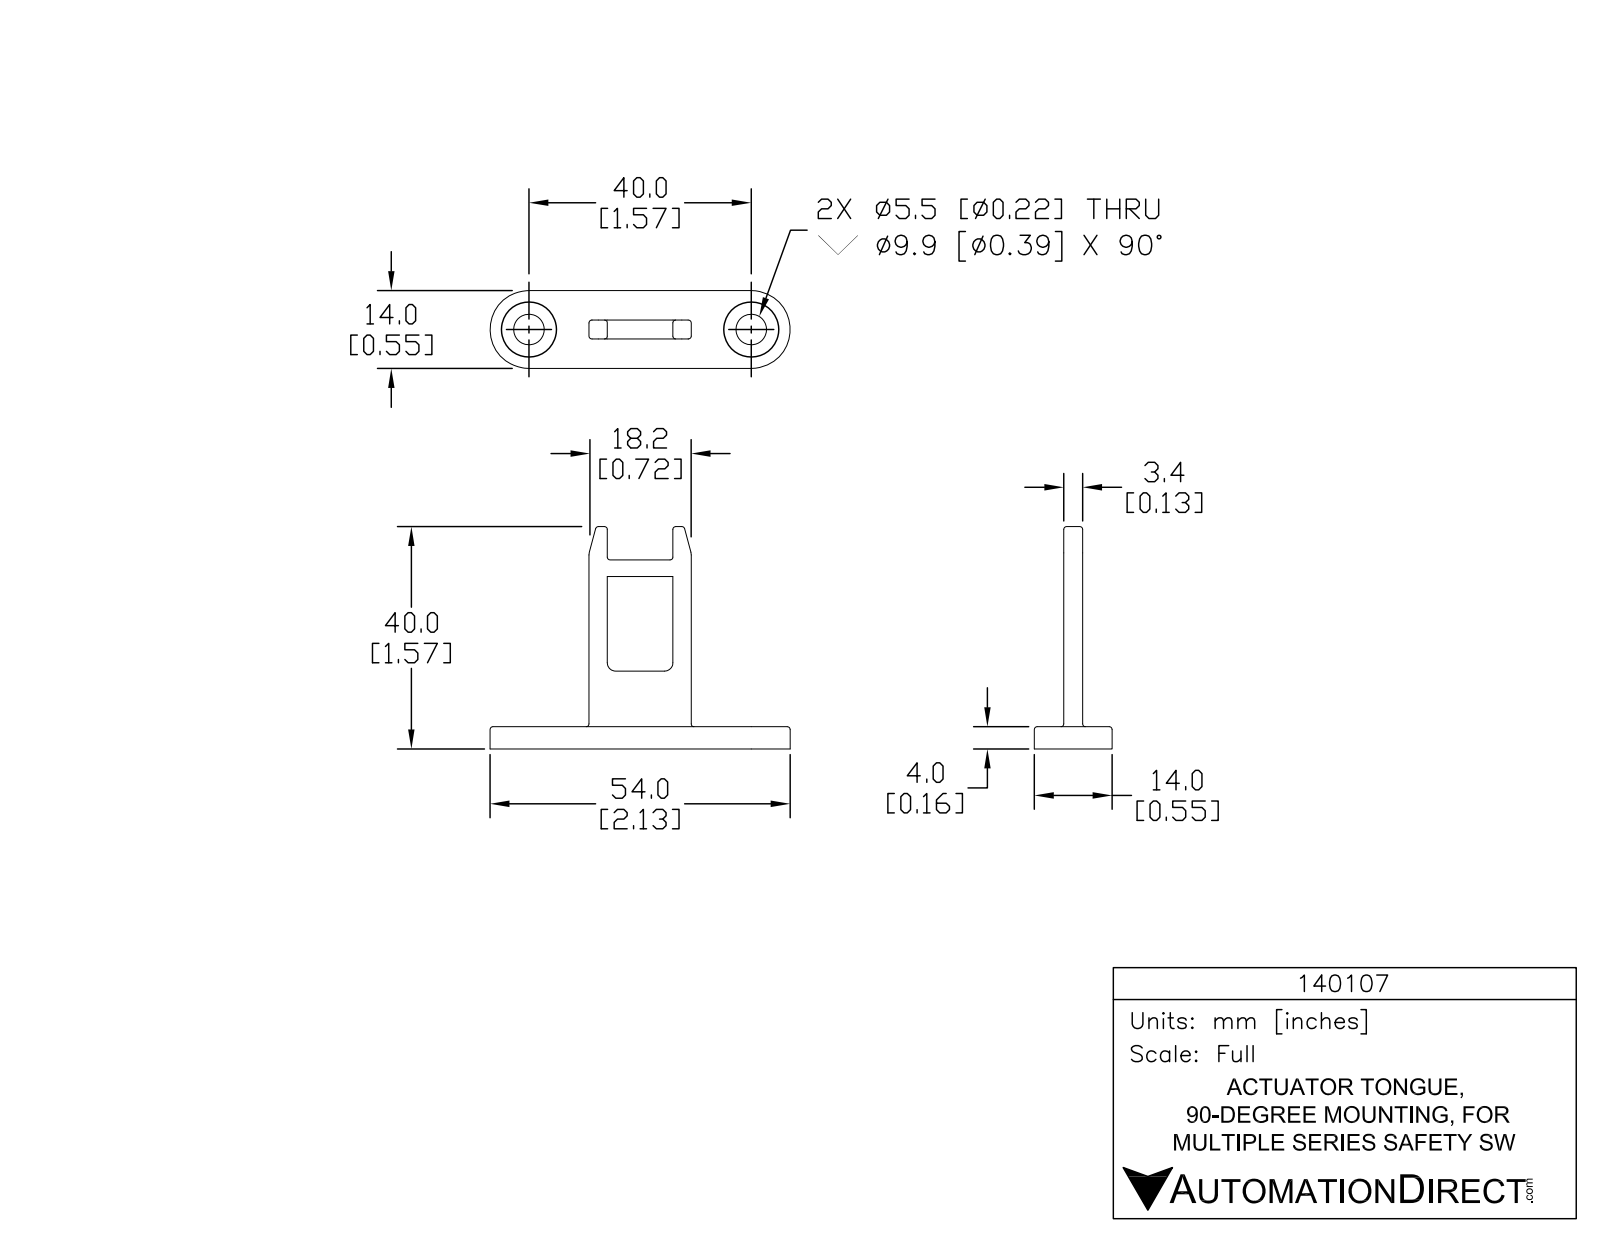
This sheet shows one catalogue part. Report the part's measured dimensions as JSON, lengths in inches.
{"part_name": "140107", "step_written_by": "SolidWorks 2017 (AUTOMOTIVE_DESIGN)", "units": "inches", "bodies": {"solids": 1, "faces": 134, "planar": 21, "cylindrical": 55, "other": 58}, "overall_size": [2.126, 1.575, 0.551], "volume_in3": 0.233, "surface_area_in2": 4.678, "round_holes": [[0.217, 2]], "partial_cylinders_radius": [[0.02, 30], [0.039, 4], [0.016, 2], [0.031, 2], [0.059, 2], [0.079, 2], [0.276, 2]], "face_to_face_distances": [0.157, 0.134, 0.209, 0.343, 0.551, 0.13, 0.594, 0.724, 0.465, 1.22], "hole_center_spacings": [1.575]}
